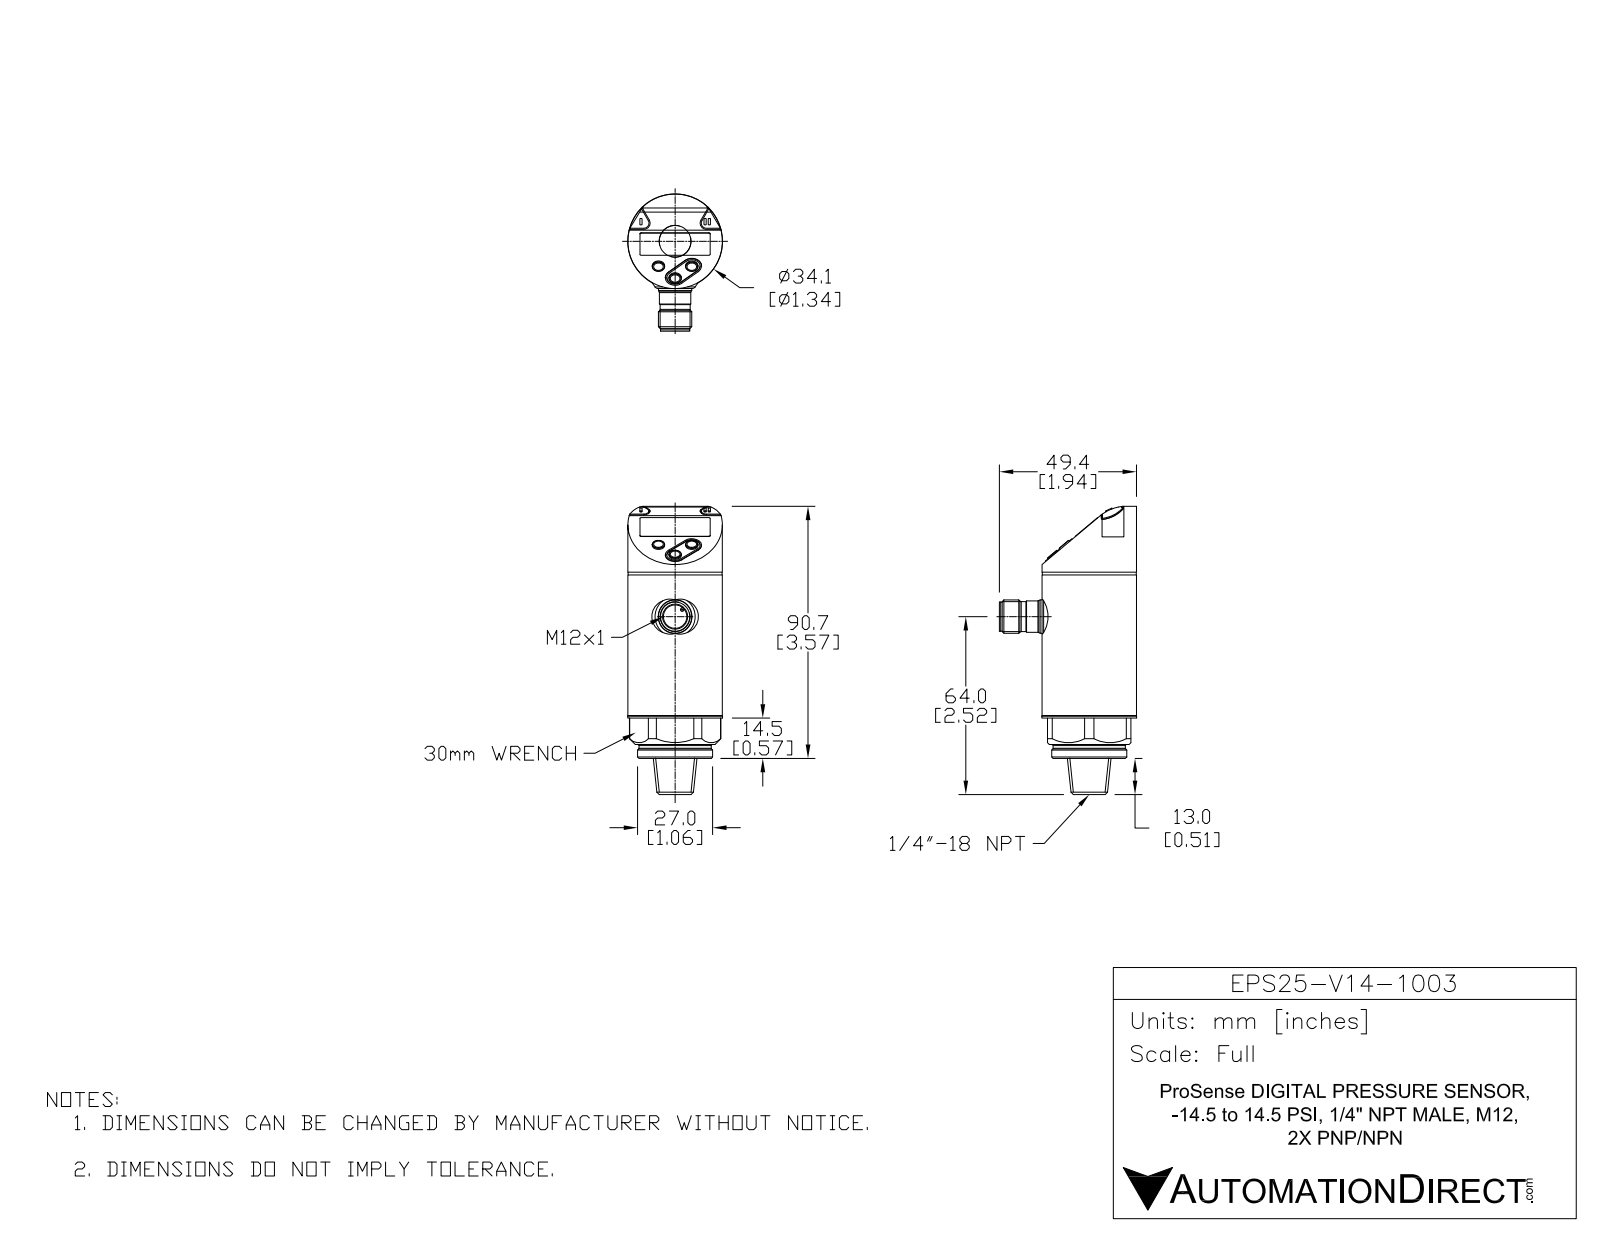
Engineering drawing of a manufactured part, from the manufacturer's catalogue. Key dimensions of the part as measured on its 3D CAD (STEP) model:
Part name (STEP PRODUCT): EPS25-V14-1003
STEP written by: SolidWorks 2016 (AUTOMOTIVE_DESIGN)
Units: millimetres
Bodies: 11 solids, 370 faces (207 planar, 84 cylindrical, 79 other)
Overall size (bounding box): 103.7 × 49.4 × 34.1
Volume: 72 203 mm³ · Surface area: 21 365 mm²
Round holes (diameter × count): ⌀4.2 ×1, ⌀8.45 ×1
Round bosses / shafts (diameter × count): ⌀1.4 ×4, ⌀1 ×4, ⌀34.1 ×1, ⌀34 ×1, ⌀33.8 ×1, ⌀27 ×1, ⌀26 ×1, ⌀12 ×1
Partial cylindrical surfaces — rounded edges, fillets, slot ends (radius × count): R1.8 ×2, R2.2 ×2, R3 ×2, R3.5 ×2, R15 ×2, R0.61 ×1, R6.8 ×1, R16.44 ×1
Main face-to-face distances: 0.68, 11.5, 12.18, 10.68, 1.5, 10, 2, 2.5, 14, 4
